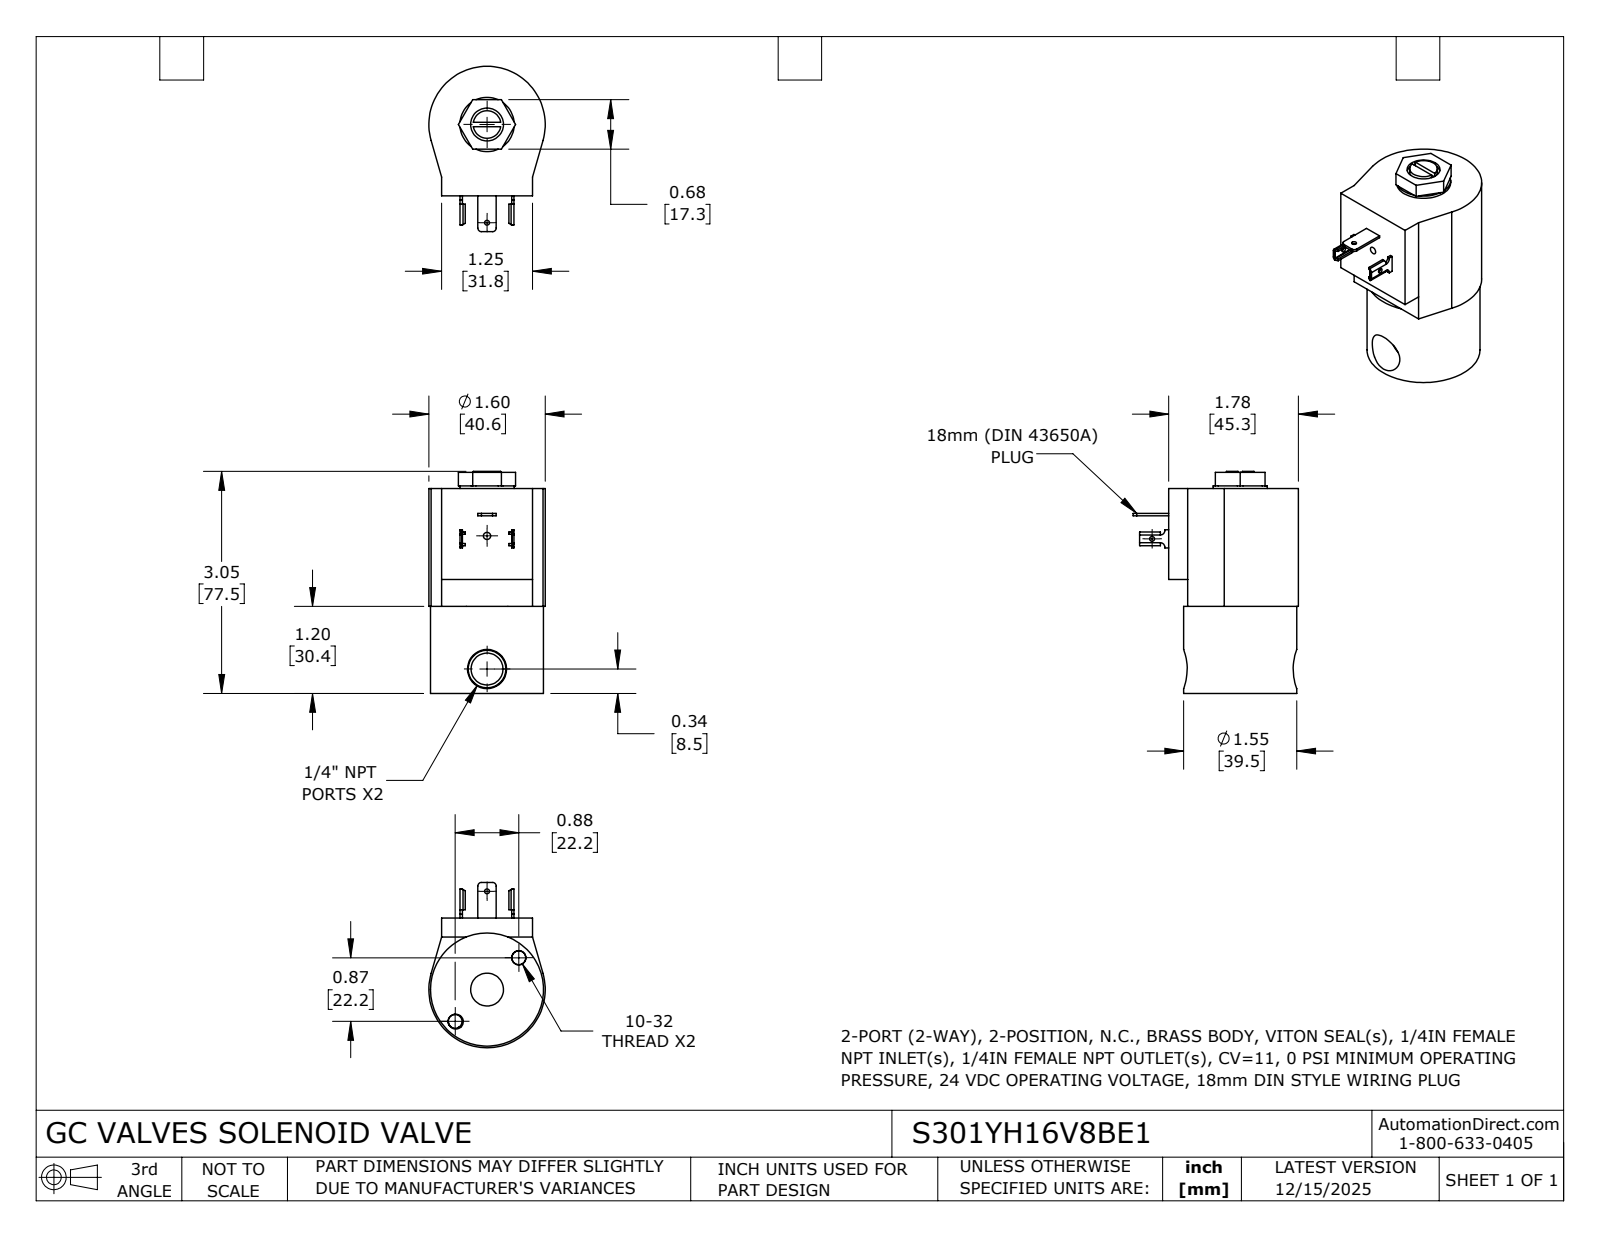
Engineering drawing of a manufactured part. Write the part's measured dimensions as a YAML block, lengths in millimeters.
part_name: "S301YH16V8BE1"
step_written_by: "SolidWorks 2024 (CONFIG_CONTROL_DESIGN)"
units: millimeters
bodies: {solids: 2, faces: 171, planar: 78, cylindrical: 71, other: 22}
overall_size: [77.7, 57.7, 40.6]
volume: 95600
surface_area: 17780
round_holes:
  - {diameter: 4.8, count: 2}
  - {diameter: 1.7, count: 1}
  - {diameter: 1.7, count: 1}
  - {diameter: 2.5, count: 1}
  - {diameter: 11.1, count: 1}
  - {diameter: 11.5, count: 1}
round_bosses_or_shafts:
  - {diameter: 39.4, count: 1}
  - {diameter: 18.9, count: 1}
  - {diameter: 9.7, count: 1}
partial_cylinders:
  - {radius: 0.2, count: 4}
  - {radius: 1, count: 4}
  - {radius: 1.3, count: 2}
  - {radius: 1.5, count: 2}
  - {radius: 20.3, count: 1}
face_to_face_distances: [41.1, 30.4, 71.5, 6.6, 39.8, 9.4, 31.8, 31.8, 77.2, 46.8]
hole_center_spacings: [15.7, 15.7, 25.7, 31.4, 34.3, 46.5, 46.7]
